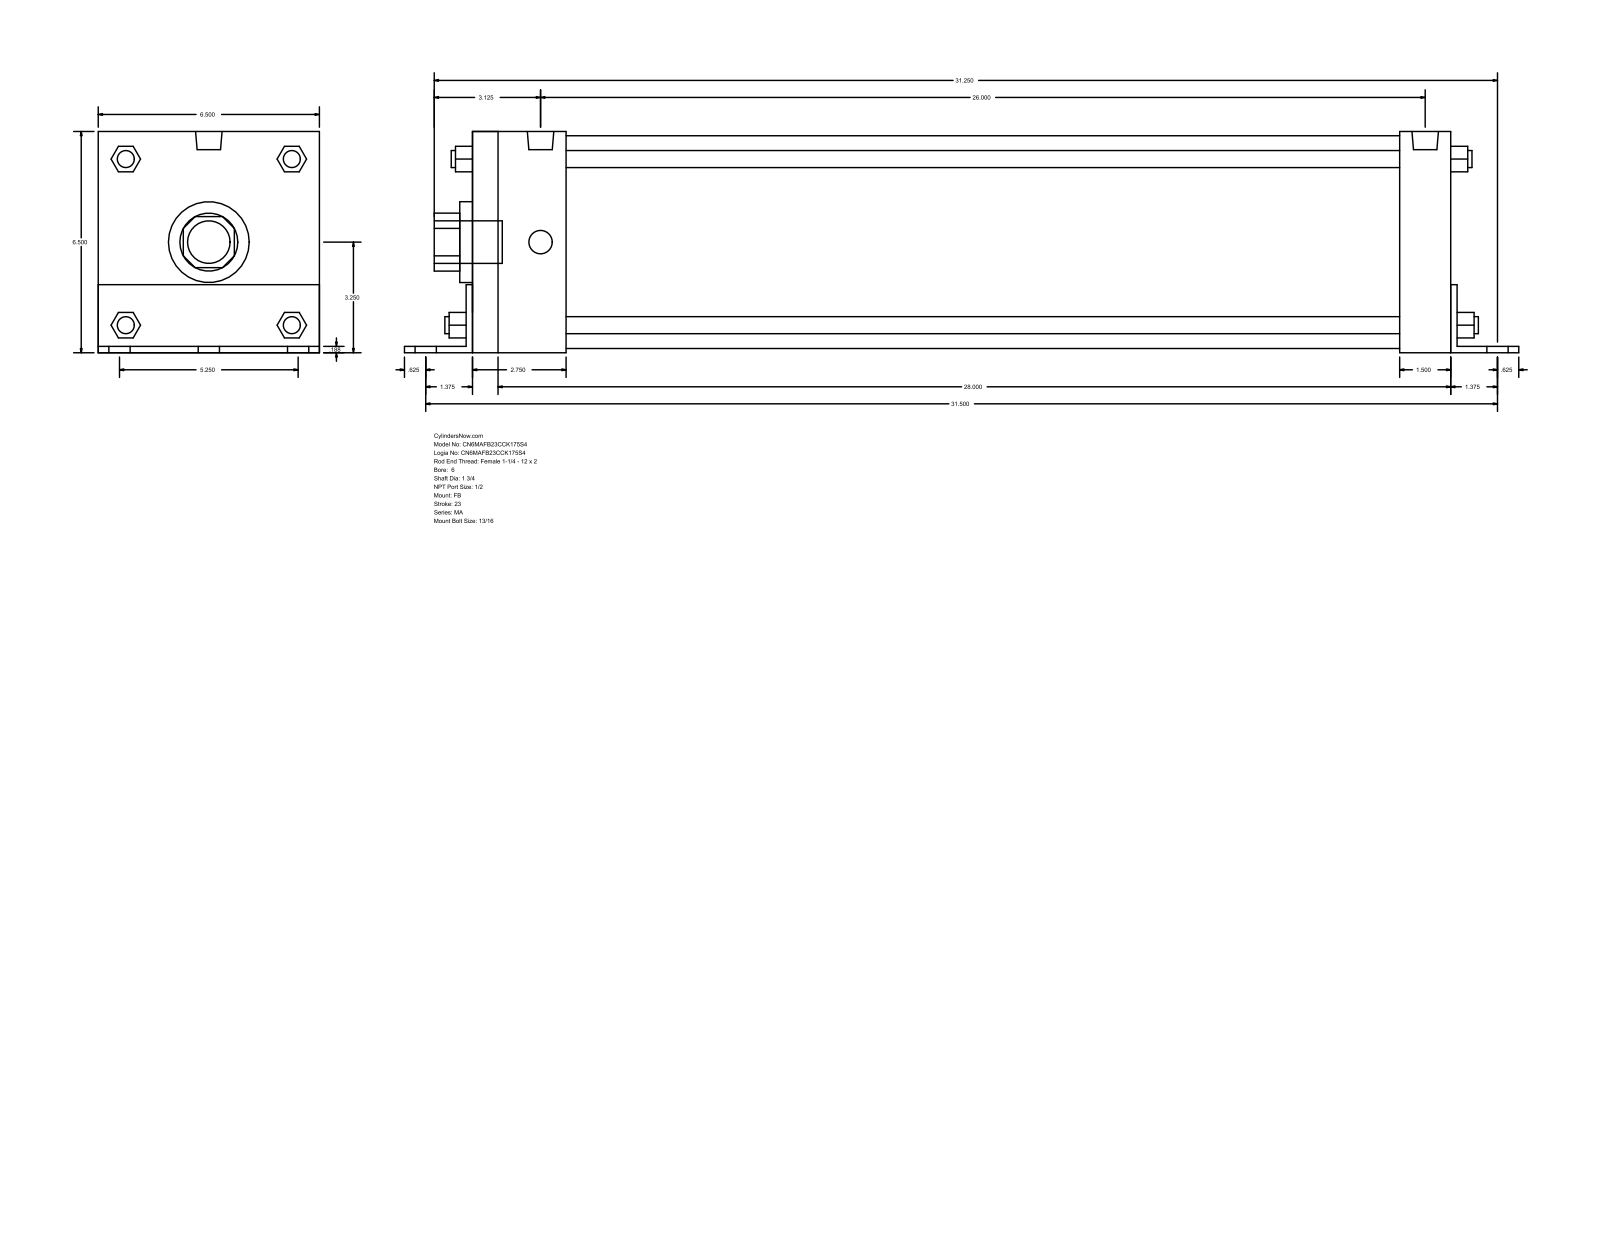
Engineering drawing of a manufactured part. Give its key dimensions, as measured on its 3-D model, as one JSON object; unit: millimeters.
{"part_name": "MA_FB__0600_1.75", "step_written_by": "GSSL Pune (CONFIG_CONTROL_DESIGN)", "units": "millimeters", "bodies": {"solids": 0, "faces": 140, "planar": 105, "cylindrical": 35, "other": 0}, "overall_size": [831.85, 165.15, 165.1], "round_holes": [[44.45, 1], [60.33, 1], [158.75, 1]], "round_bosses_or_shafts": [[20.64, 6], [17.46, 4], [12.7, 4], [19.77, 2], [31.75, 1]], "partial_cylinders_radius": [[21.63, 1], [32.05, 1]], "face_to_face_distances": [165.1, 4.76, 730.26, 165.15, 735.02, 4.71, 160.39, 739.78, 38.1, 42.86]}
